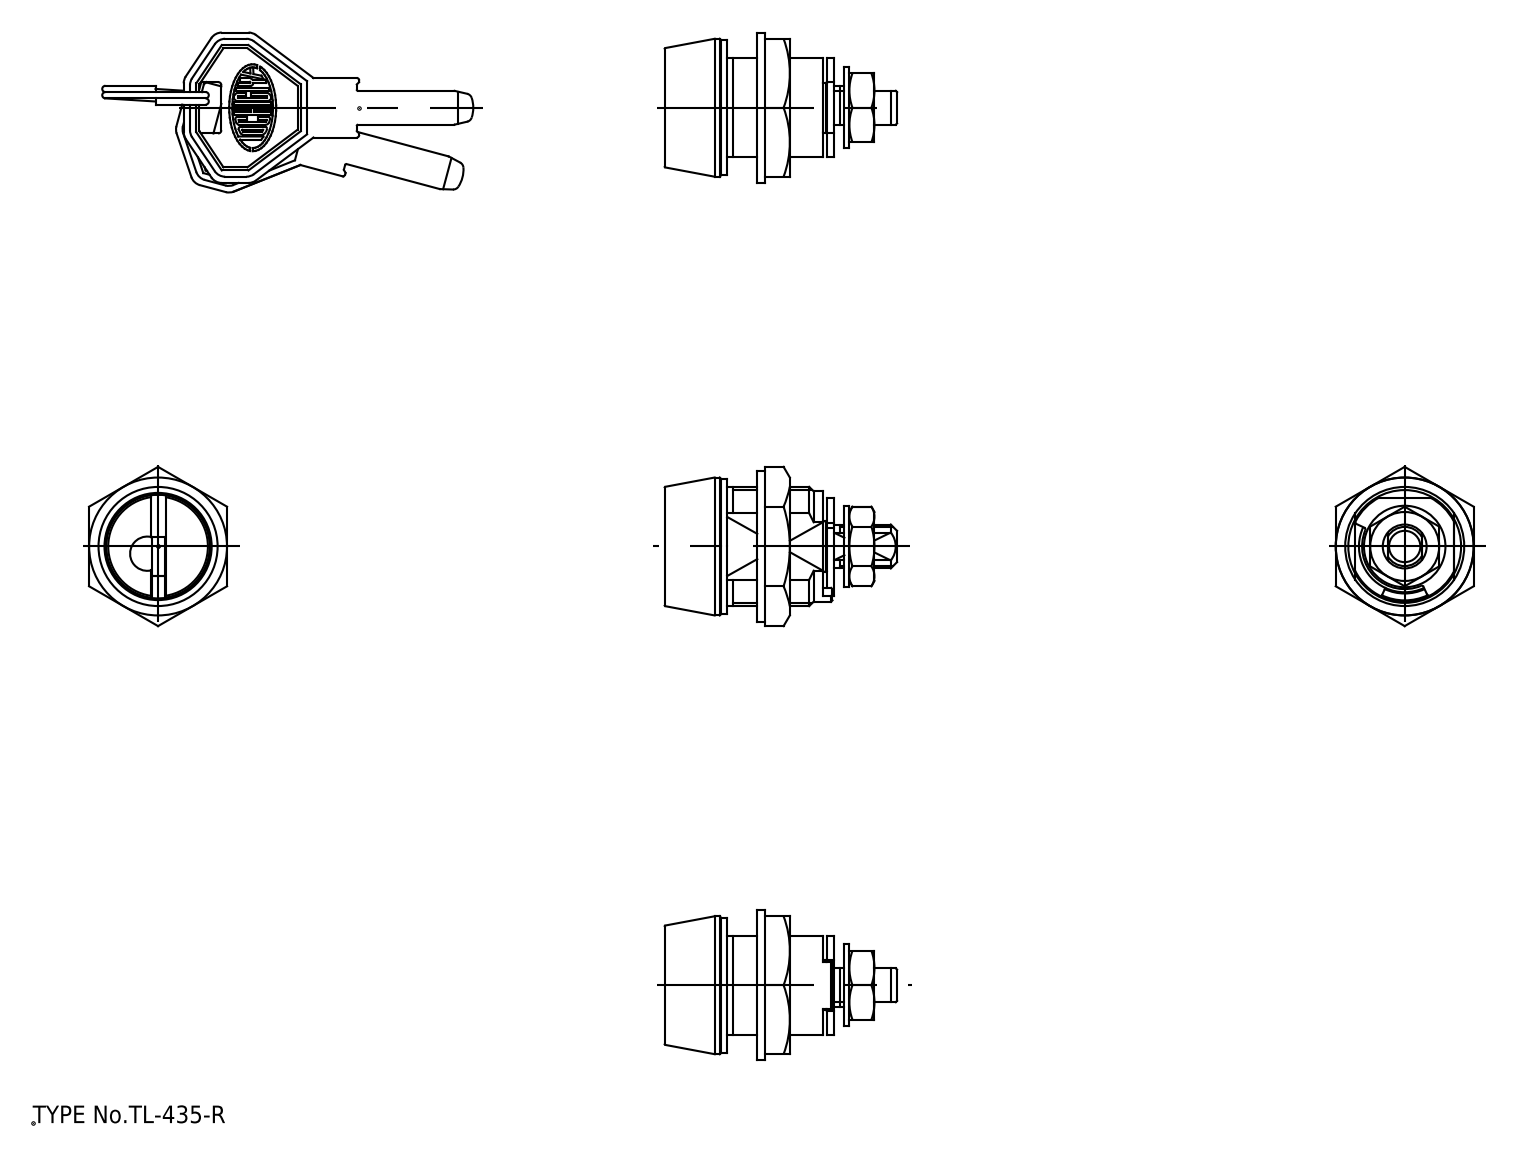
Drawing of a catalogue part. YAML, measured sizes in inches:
part_name: "FWP21S組立図-提出用3Dモデル_M1; FWP21S組立図-提出用3Dモデル_M2; FWP21S組立図-提出用3Dモデル_M3; FWP21S組立図-提出用3Dモデル_M4 (+2 more)"
step_written_by: "spGate 15.6.1 (AUTOMOTIVE_DESIGN)"
units: inches
bodies: {solids: 6, faces: 153, planar: 68, cylindrical: 50, other: 35}
overall_size: [1.461, 1, 0.945]
volume: 0.546
surface_area: 7.679
round_holes:
  - {diameter: 0.276, count: 1}
  - {diameter: 0.724, count: 1}
  - {diameter: 0.756, count: 1}
round_bosses_or_shafts:
  - {diameter: 0.945, count: 1}
  - {diameter: 0.866, count: 1}
  - {diameter: 0.846, count: 1}
  - {diameter: 0.512, count: 1}
  - {diameter: 0.315, count: 1}
partial_cylinders:
  - {radius: 0.146, count: 1}
  - {radius: 0.211, count: 1}
  - {radius: 0.268, count: 1}
  - {radius: 0.313, count: 1}
  - {radius: 0.346, count: 1}
  - {radius: 0.374, count: 1}
face_to_face_distances: [0.563, 0.047, 0.642, 0.102, 0.539, 1.067, 0.744, 0.354, 0.713, 0.15]
